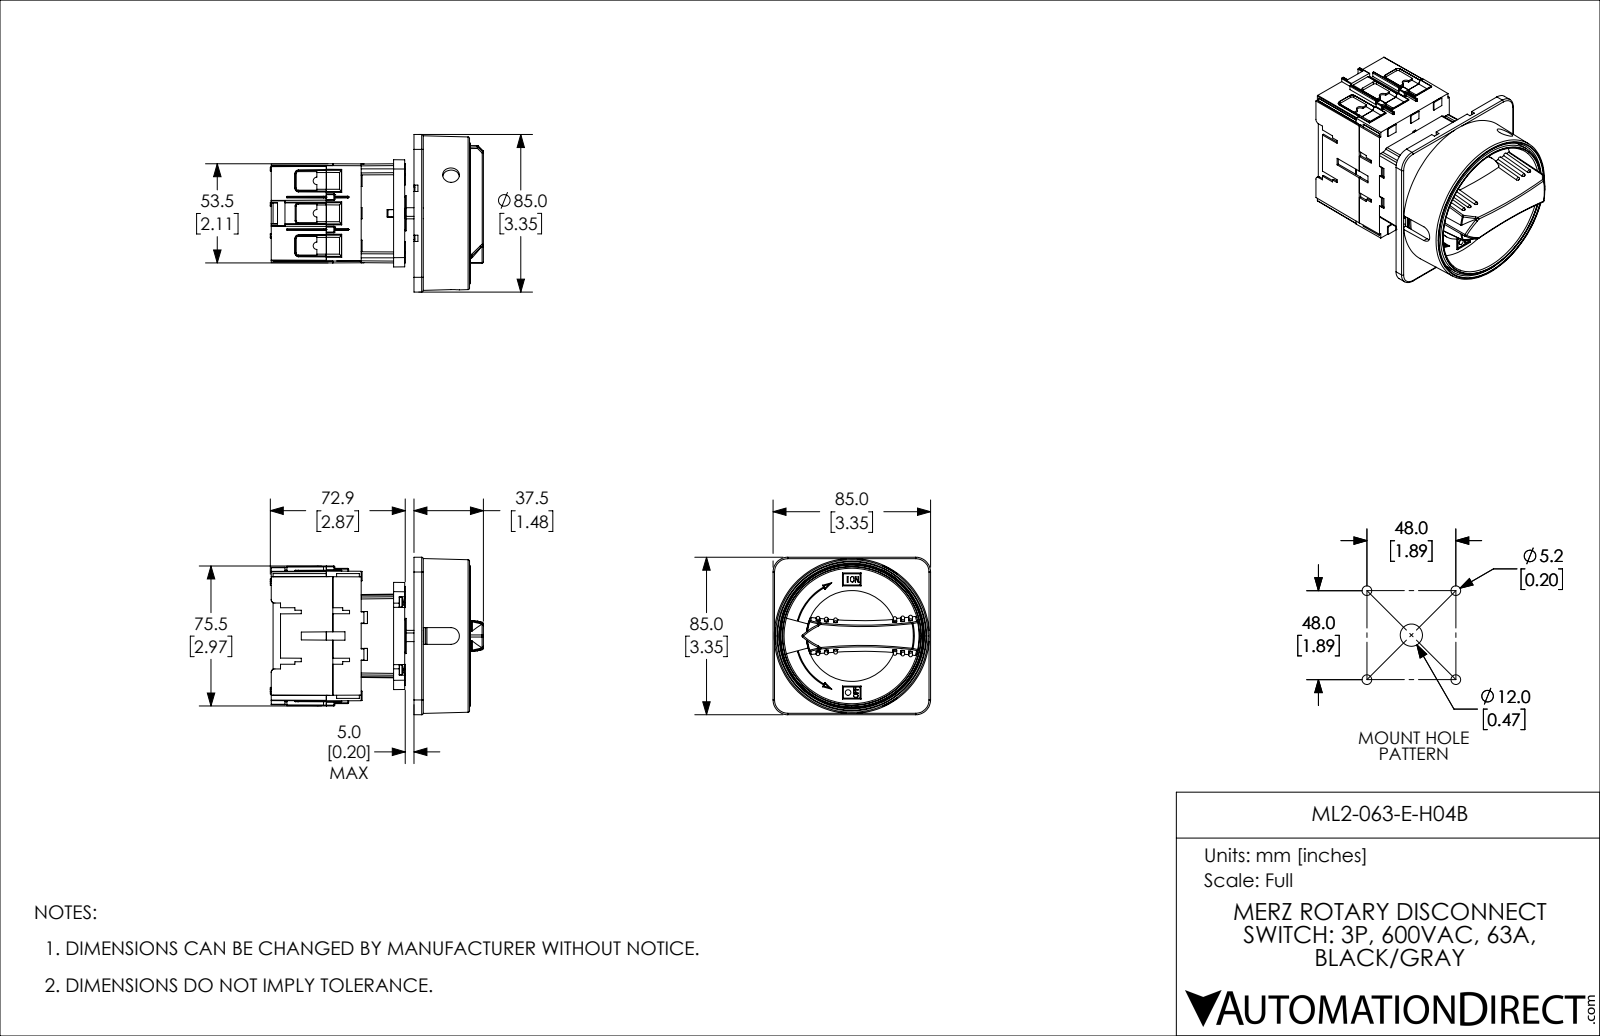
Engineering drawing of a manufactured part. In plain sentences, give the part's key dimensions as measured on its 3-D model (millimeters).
The part is named "ML2-063-E-H04B". Its 3-D file was written by "SolidWorks 2019 (AUTOMOTIVE_DESIGN)". It is 1 solid with 1874 faces: 1179 planar, 337 cylindrical and 358 other. Overall it measures 115.1 by 85 by 85 millimeters. Its volume is 304 100 cubic millimeters and its surface area 102 000 square millimeters. Round holes: 2 of diameter 9, 1 of diameter 45, 1 of diameter 73.1. Round bosses or shafts: 6 of diameter 5.4, 4 of diameter 5.5, 4 of diameter 5.2, 1 of diameter 77, 1 of diameter 76.5, 1 of diameter 49, 1 of diameter 47.5, 1 of diameter 19. Partial cylindrical surfaces (rounded edges, fillets, slot ends): 43 of radius 0.3, 29 of radius 0.5, 28 of radius 0.4, 14 of radius 0.3, 11 of radius 2, 8 of radius 0.7, 4 of radius 0.8, 4 of radius 1. The main face-to-face distances are 3.5, 8.5, 6, 2, 5, 12, 1, 6.5, 71, 7.
